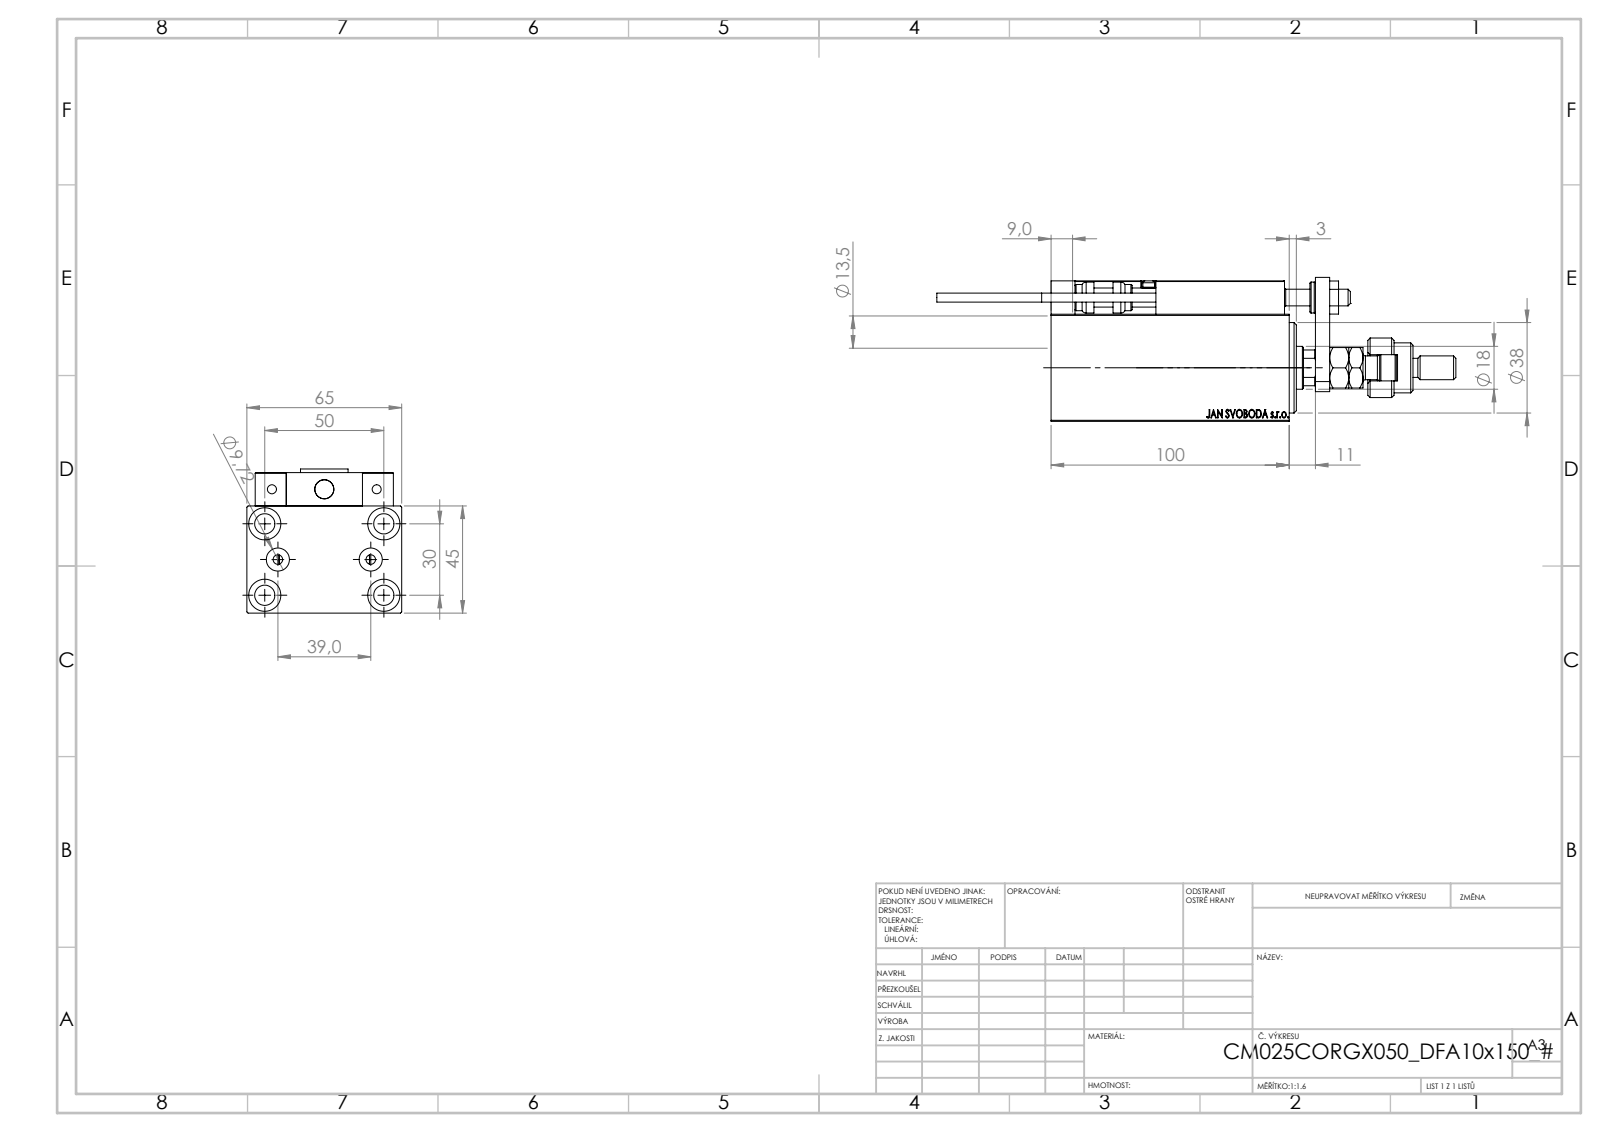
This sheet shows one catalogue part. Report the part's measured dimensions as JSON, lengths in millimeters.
{"part_name": "ZARAZKA; KONCOVKA; SWITCH DIM B,W; MAGNET (+8 more)", "step_written_by": "SolidWorks 2019 (CONFIG_CONTROL_DESIGN)", "units": "millimeters", "bodies": {"solids": 25, "faces": 1363, "planar": 588, "cylindrical": 197, "other": 578}, "overall_size": [218, 65, 60.5], "volume_mm3": 310375, "surface_area_mm2": 90735, "round_holes": [[4, 6], [8, 5], [8.5, 5], [3.2, 4], [13.5, 4], [5, 2], [9.72, 2], [7, 1], [14.5, 1], [18, 1], [21.5, 1], [27, 1]], "round_bosses_or_shafts": [[5, 2], [3.8, 2], [25, 1], [21, 1], [16, 1], [13, 1], [11, 1], [10, 1]], "partial_cylinders_radius": [[0.3, 30], [3, 2], [5.5, 1], [8.5, 1], [8.75, 1]], "face_to_face_distances": [45, 65, 14, 6, 59, 3, 7, 89, 5, 111], "hole_center_spacings": [15.98, 29.15, 46.96, 11.37, 19.5, 20, 28.9, 29.59]}
